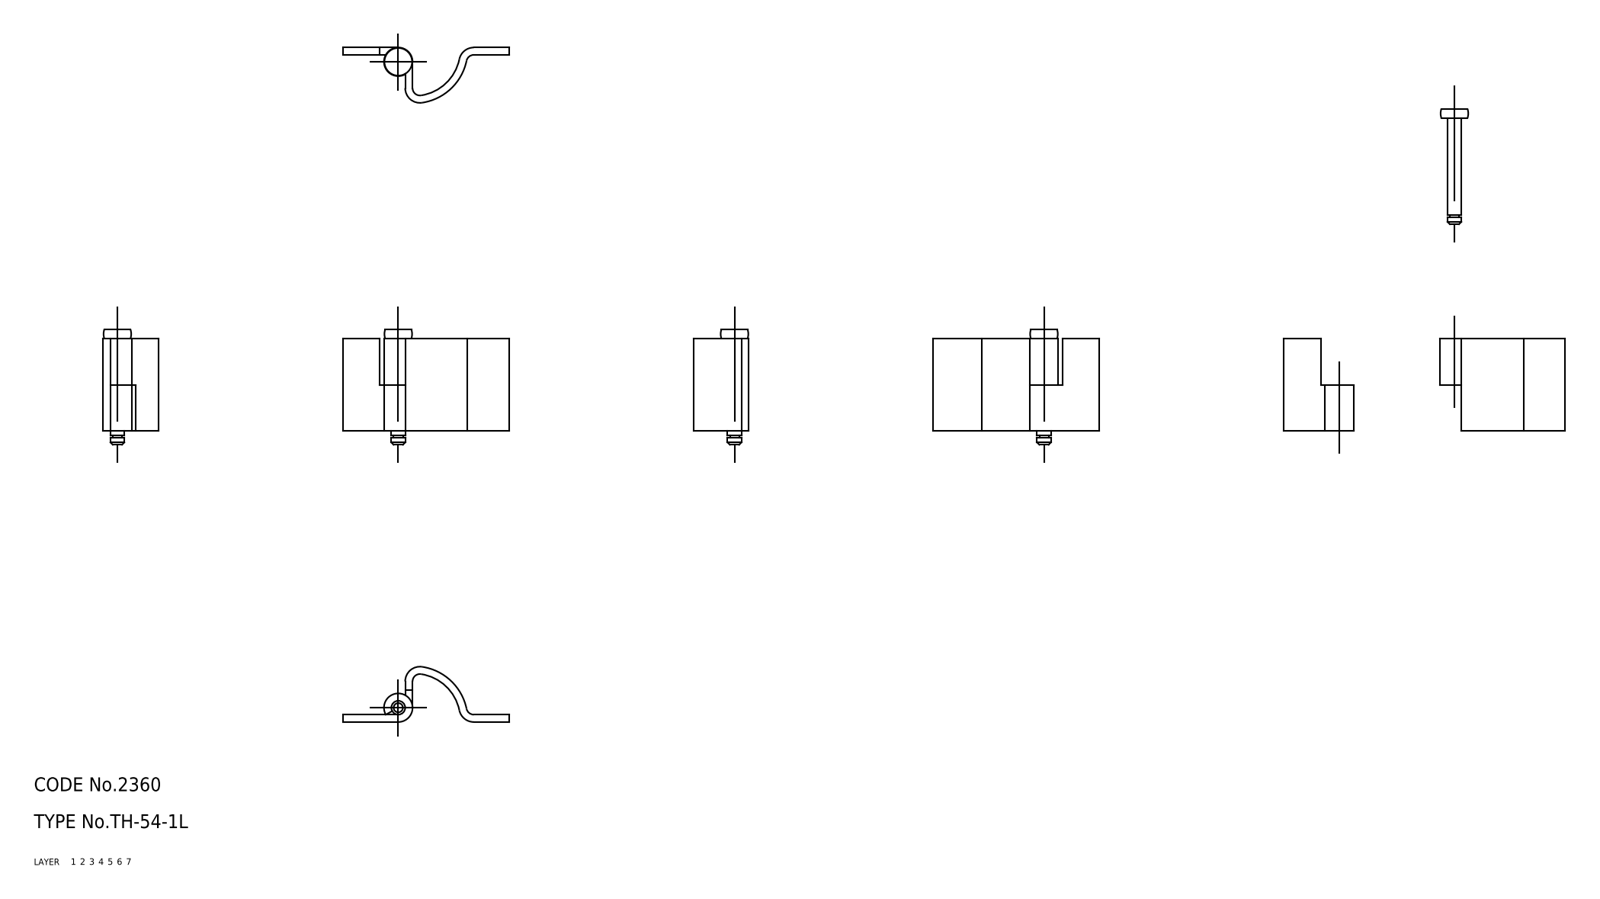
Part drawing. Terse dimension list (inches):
name: shaft; hinge piece_B; hinge piece_A; TH_54_1_L_10881_36
written by: CADfix (AUTOMOTIVE_DESIGN)
unit: in
bodies: 3 solids, 42 faces (0 planar, 0 cylindrical, 42 other)
size: 1.417 × 0.984 × 0.472
volume: 0.118 in³; area: 4.362 in²
